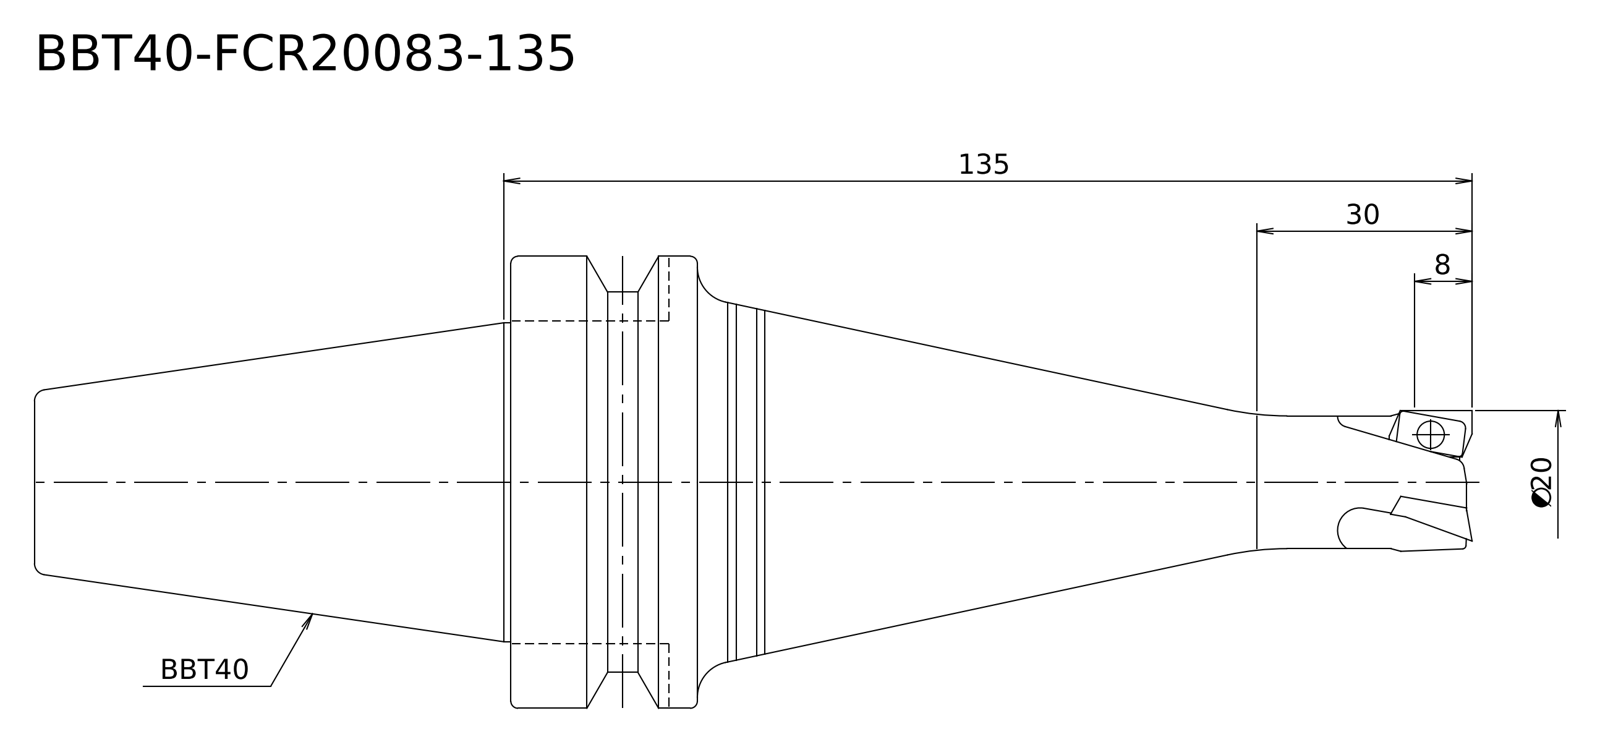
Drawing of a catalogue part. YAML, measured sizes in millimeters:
step_written_by: "Kubotek KeyCreator V8.5.1 (14335) (CONFIG_CONTROL_DESIGN)"
units: millimeters
bodies: {solids: 1, faces: 17, planar: 4, cylindrical: 6, other: 7}
overall_size: [200.4, 63, 63]
volume: 242898
surface_area: 28113
round_bosses_or_shafts:
  - {diameter: 63, count: 1}
  - {diameter: 53, count: 1}
  - {diameter: 44.45, count: 1}
  - {diameter: 25, count: 1}
  - {diameter: 23.5, count: 1}
face_to_face_distances: [66.4, 134, 200.4, 108, 26, 92.4]
